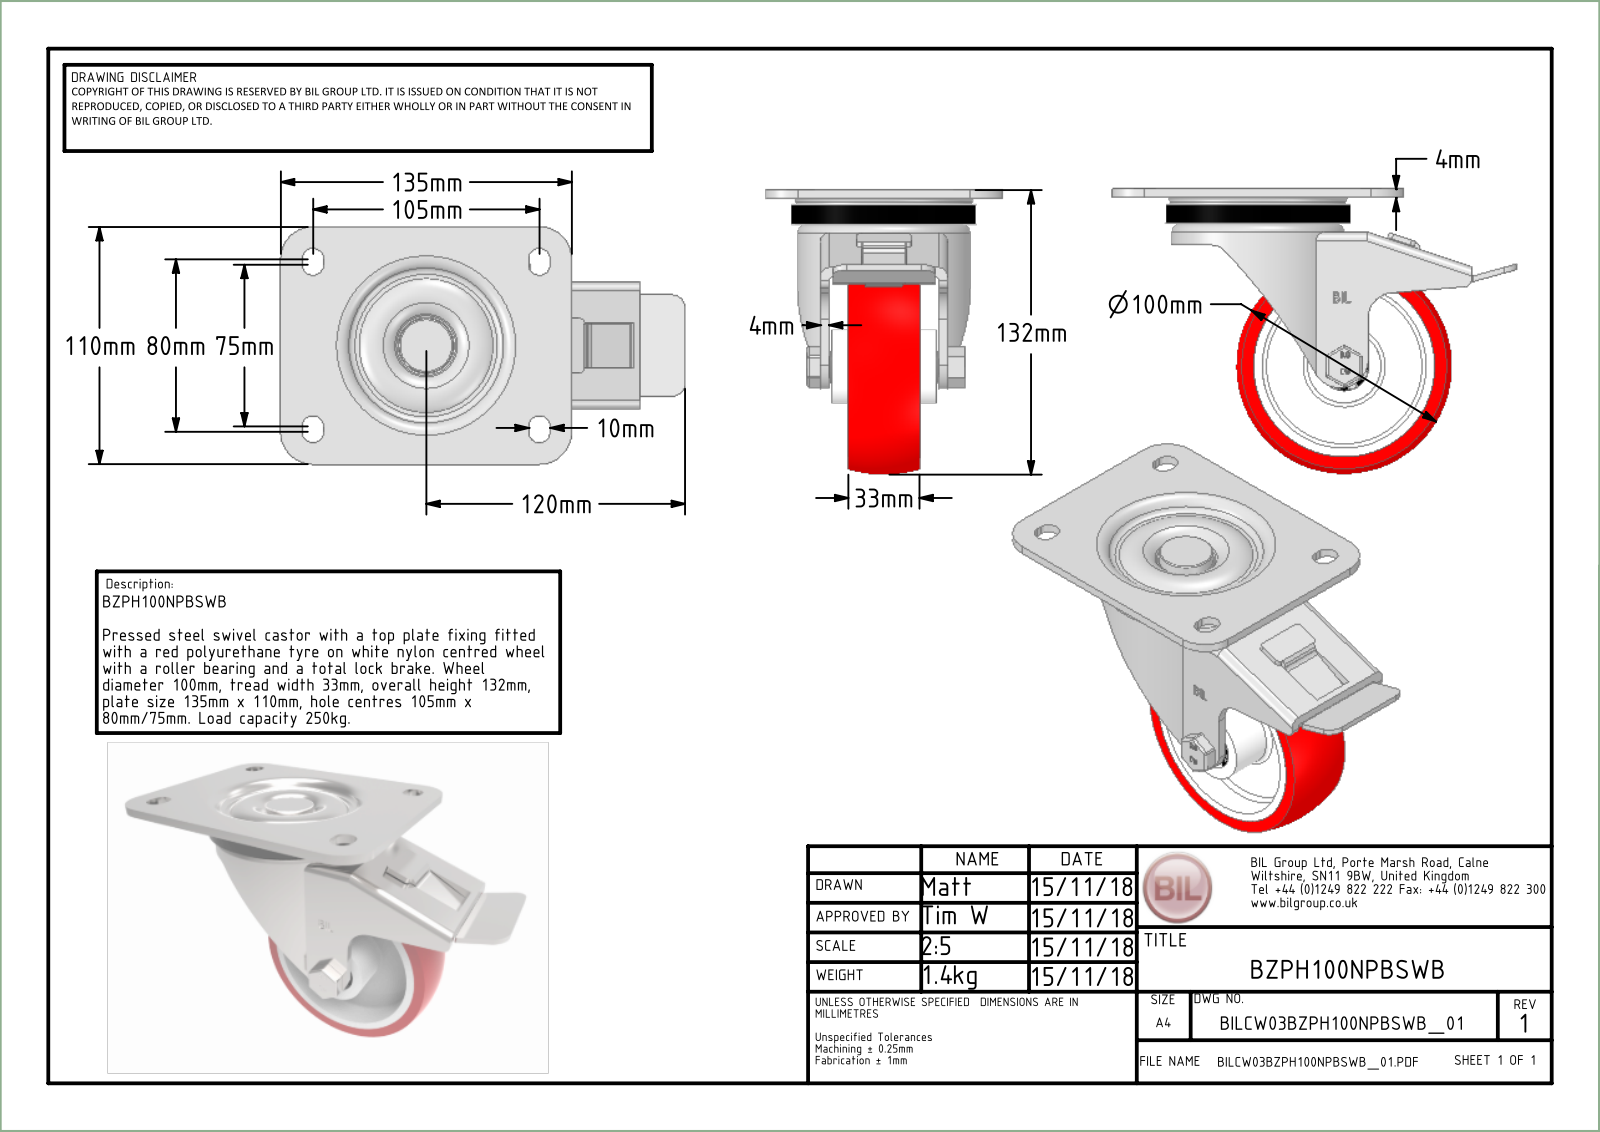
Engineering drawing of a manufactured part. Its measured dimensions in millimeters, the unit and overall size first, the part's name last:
Units: millimetres
Overall size (bounding box): 187.5 × 132 × 110
Round holes (diameter × count): ⌀8 ×1, ⌀10 ×1, ⌀10.2 ×1, ⌀10.5 ×1, ⌀12 ×1, ⌀15 ×1, ⌀15.5 ×1, ⌀23.5 ×1, ⌀26 ×1, ⌀27 ×1, ⌀28 ×1, ⌀72 ×1
Round bosses / shafts (diameter × count): ⌀4 ×8, ⌀83.5 ×1, ⌀80 ×1, ⌀60 ×1, ⌀51 ×1, ⌀32 ×1, ⌀30.5 ×1, ⌀26.9 ×1
Partial cylindrical surfaces — rounded edges, fillets, slot ends (radius × count): R0.5 ×27, R2 ×15, R0.75 ×10, R4 ×10, R5.5 ×8, R1.5 ×7, R1.25 ×4, R3 ×4
Main face-to-face distances: 4, 9, 27.5, 13, 19, 15, 31.5, 12.5, 46.5, 23.5
Volume: 347 680 mm³ · Surface area: 171 277 mm²
Bodies: 23 solids, 733 faces (432 planar, 207 cylindrical, 94 other)
Part name (STEP PRODUCT): BZPH100NPBSWB v3; BZPH100ASSWB v1; ZINC PLATED, PRESSED STEEL TOP PLATE; ZINC PLATED, PRESSED STEEL FORKS (+8 more)
STEP written by: Autodesk Translation Framework v14.10.0.0 (AUTOMOTIVE_DESIGN)
